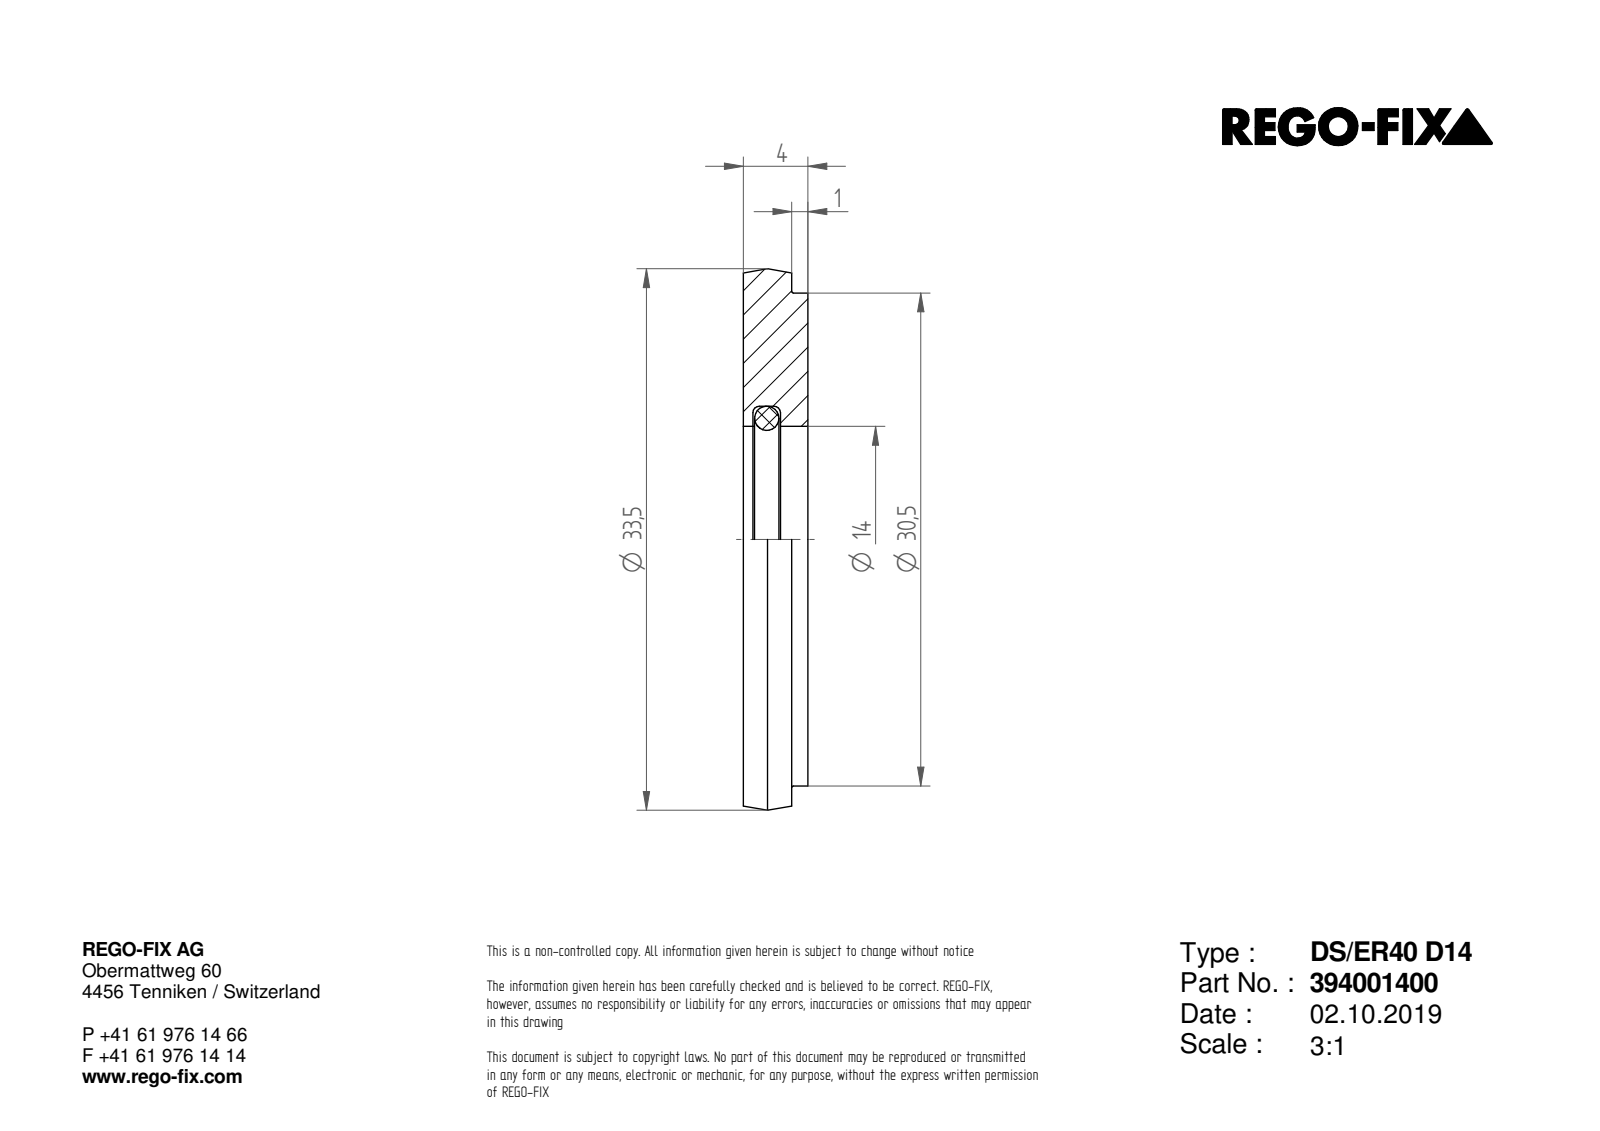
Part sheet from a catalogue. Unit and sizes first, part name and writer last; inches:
Units: inches
Overall size (bounding box): 1.319 × 1.319 × 0.157
Round holes (diameter × count): ⌀0.551 ×1
Round bosses / shafts (diameter × count): ⌀1.319 ×1, ⌀1.201 ×1
Main face-to-face distances: 0.157, 0.039, 0.118
Volume: 0.168 in³ · Surface area: 3.159 in²
Bodies: 1 solid, 7 faces (3 planar, 3 cylindrical, 1 other)
Part name (STEP PRODUCT): NOCUT
STEP written by: SIEMENS PLM Software Solid Edge ST10 (AUTOMOTIVE_DESIGN)
